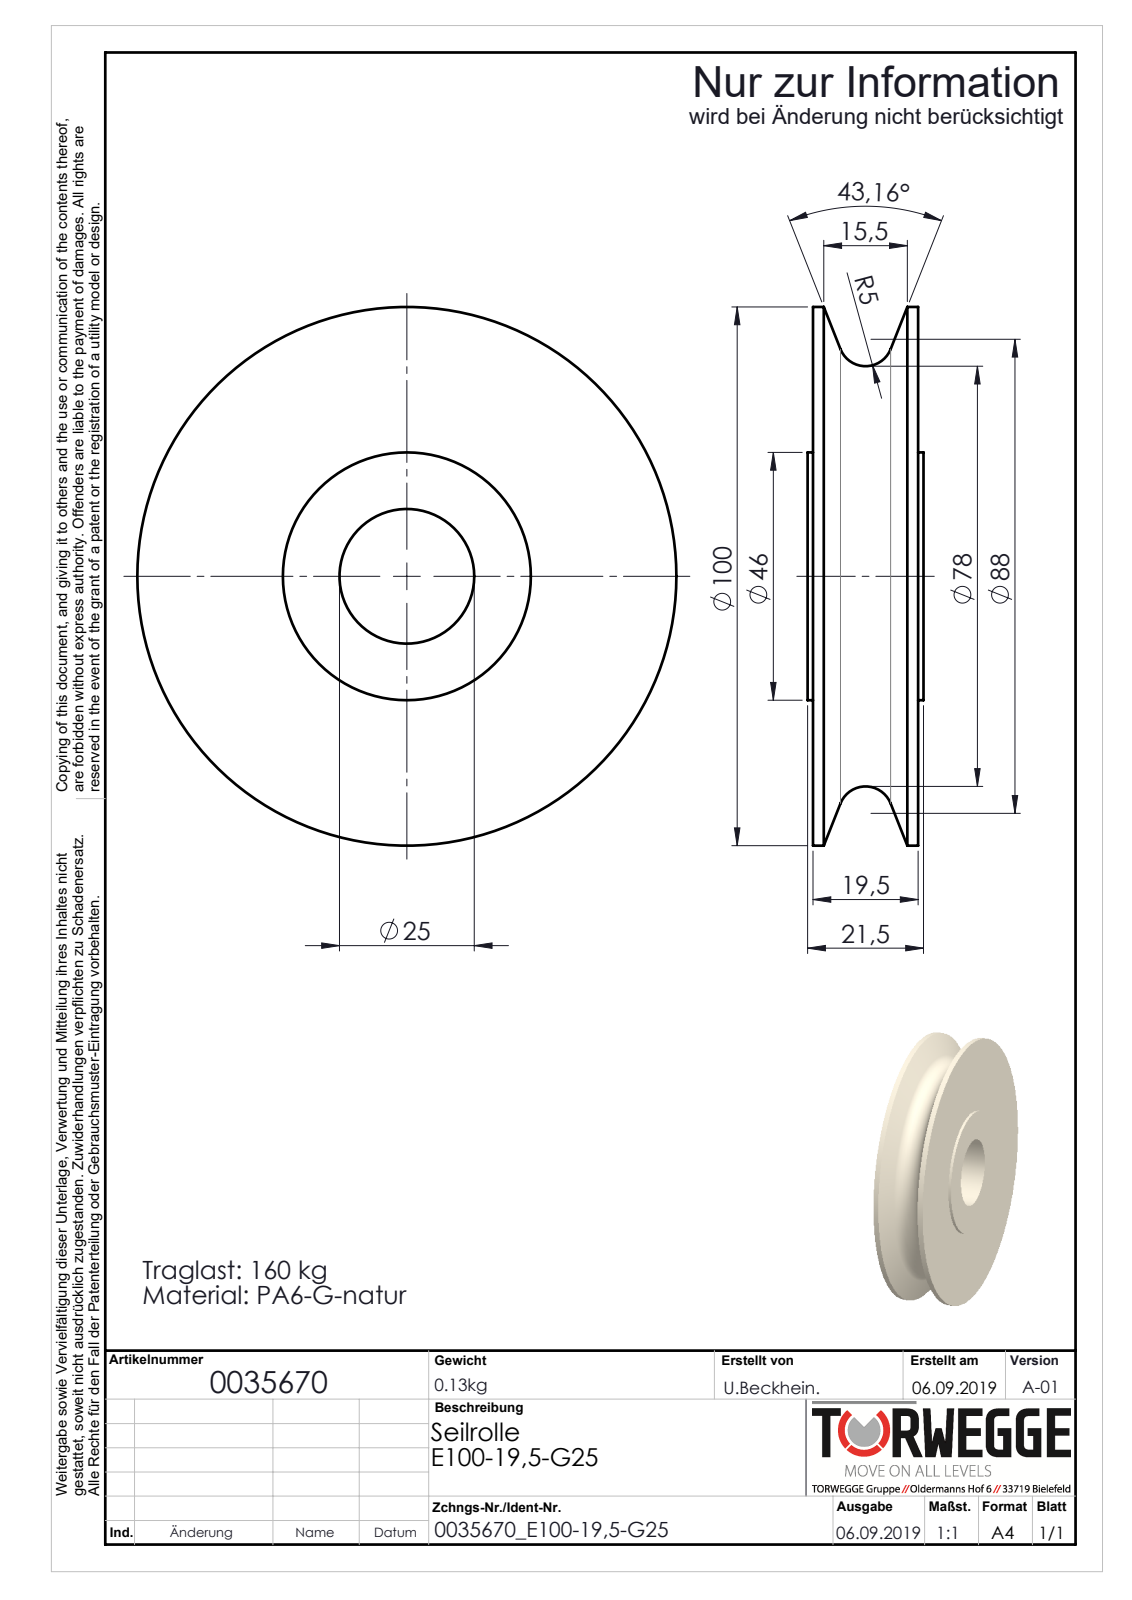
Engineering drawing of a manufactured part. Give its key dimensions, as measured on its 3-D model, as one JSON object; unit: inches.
{"part_name": "0035670_E100-19,5-G25_(A-01)", "step_written_by": "SolidWorks 2018 (AUTOMOTIVE_DESIGN)", "units": "inches", "bodies": {"solids": 1, "faces": 22, "planar": 4, "cylindrical": 10, "other": 8}, "overall_size": [3.937, 3.937, 0.846], "volume_in3": 6.841, "surface_area_in2": 40.07, "round_holes": [[0.984, 1]], "round_bosses_or_shafts": [[3.937, 1], [1.811, 1]], "face_to_face_distances": [0.768, 0.039, 0.807, 0.846]}
